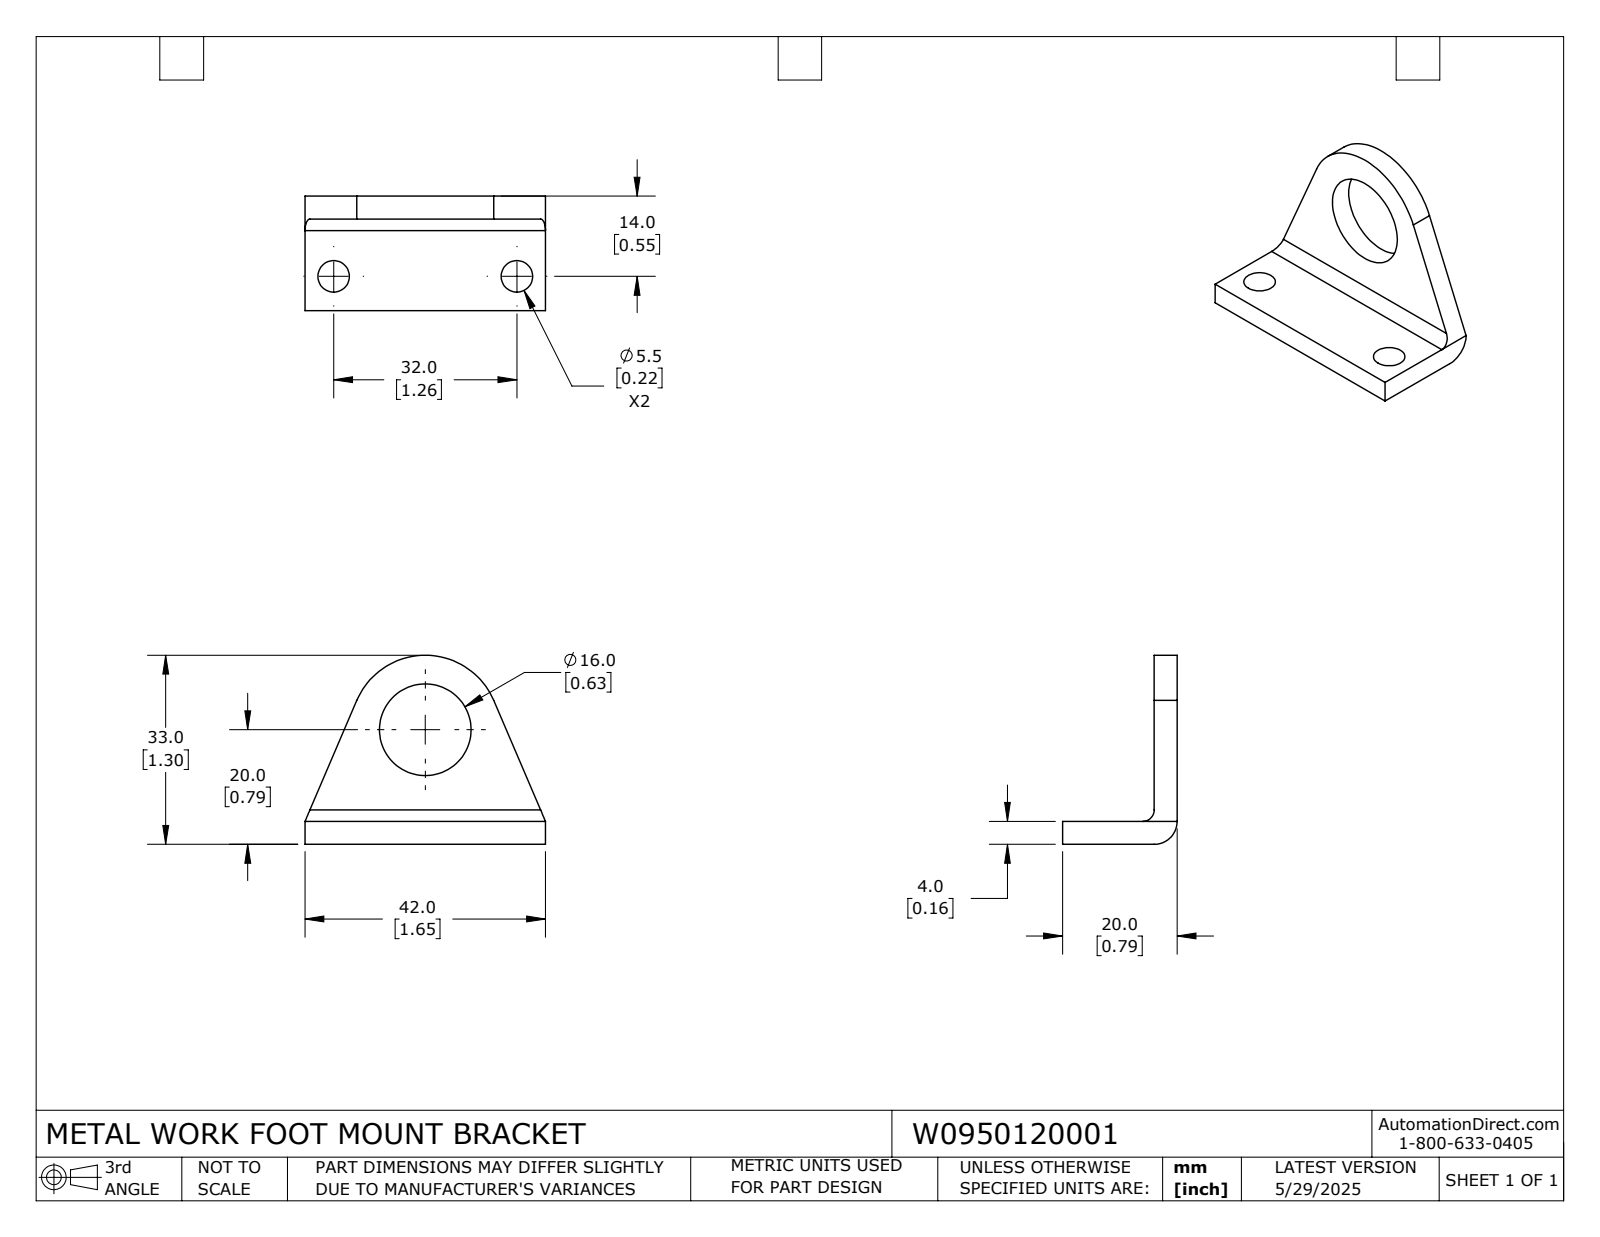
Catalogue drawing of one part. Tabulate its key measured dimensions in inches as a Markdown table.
| quantity | value |
| --- | --- |
| part name | W0950120001 |
| STEP written by | SolidWorks 2024 (CONFIG_CONTROL_DESIGN) |
| units | inches |
| bodies | 1 solid, 18 faces (9 planar, 9 cylindrical, 0 other) |
| overall size | 1.654 × 1.299 × 0.787 |
| volume | 0.341 in³ |
| surface area | 5.743 in² |
| round holes (diameter × count) | 0.217 × 2, 0.63 × 1 |
| partial cylindrical surfaces (radius × count) | 0.079 × 1, 0.157 × 1, 0.512 × 1 |
| main face-to-face distances | 0.157, 0.787, 0.63, 1.654 |
| hole center spacings | 1.26 |
